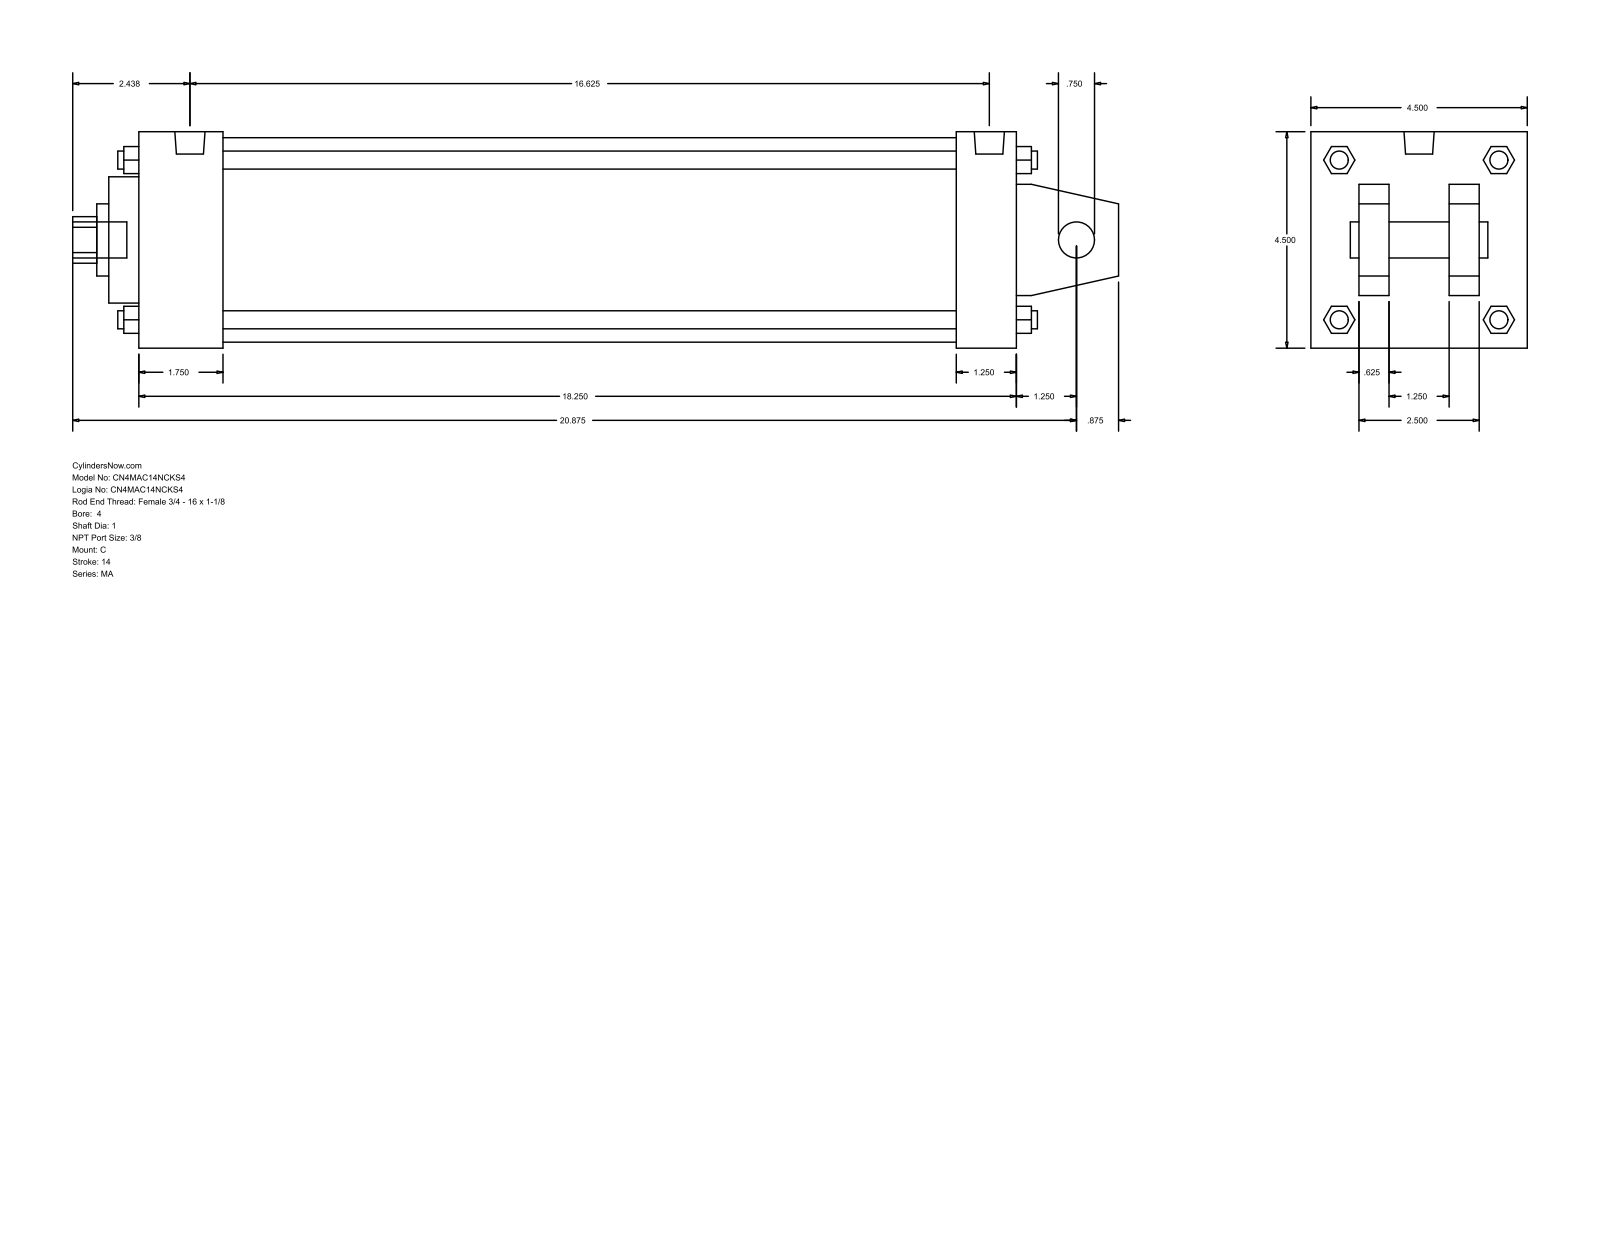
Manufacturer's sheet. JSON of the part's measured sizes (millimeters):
{"part_name": "MA_C__0400_1", "step_written_by": "GSSL Pune (CONFIG_CONTROL_DESIGN)", "units": "millimeters", "bodies": {"solids": 0, "faces": 141, "planar": 109, "cylindrical": 32, "other": 0}, "overall_size": [552.45, 114.3, 114.3], "round_holes": [[19.05, 1], [25.4, 1], [38.1, 1], [66.67, 1], [107.95, 1]], "round_bosses_or_shafts": [[11.11, 4], [9.53, 4], [15.93, 2], [19.05, 1]], "partial_cylinders_radius": [[12.29, 1]], "face_to_face_distances": [114.3, 463.56, 15.87, 73.03, 41.27, 25.4, 88.9, 47.63, 431.81, 31.75]}
